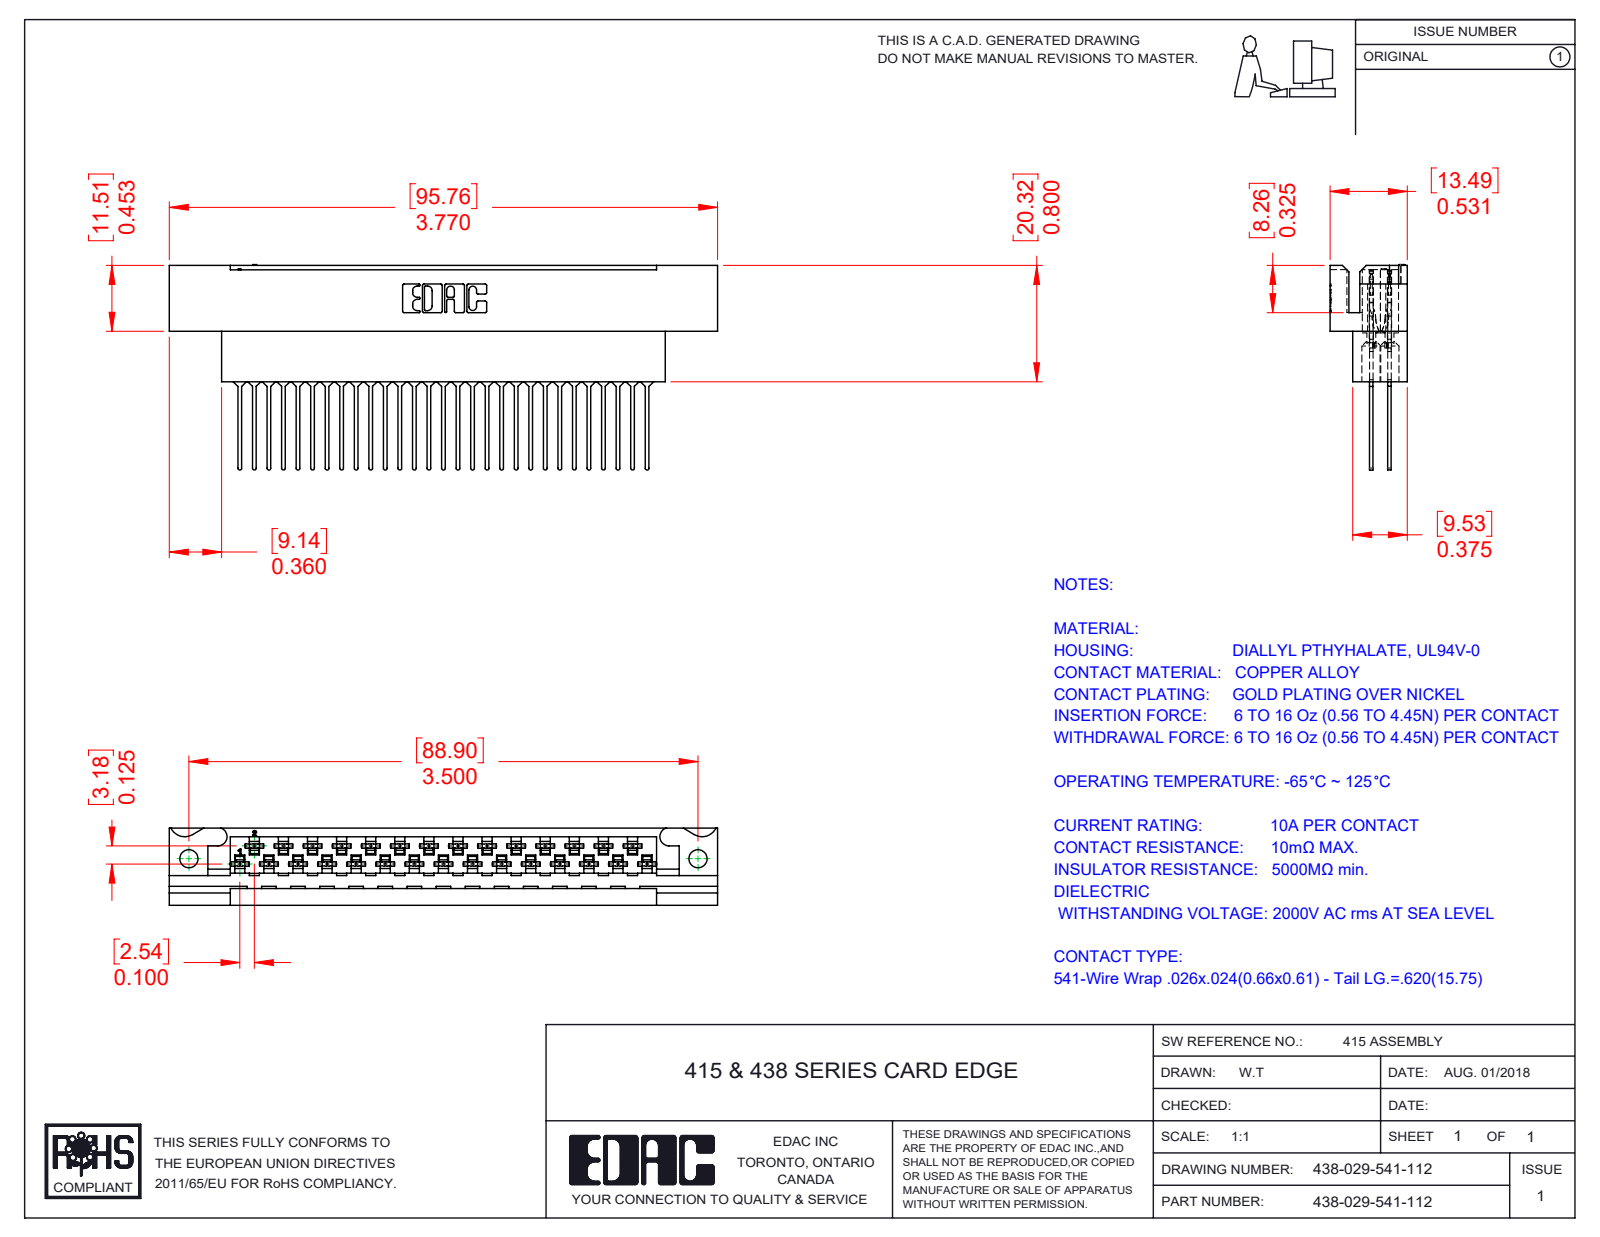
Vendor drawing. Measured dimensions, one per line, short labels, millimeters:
name: 438-210-001_438-210-029-112; 438-029-541-112; 516-290-001_541
written by: SolidWorks 2016 (CONFIG_CONTROL_DESIGN)
unit: mm
bodies: 30 solids, 2998 faces (1911 planar, 804 cylindrical, 283 other)
size: 95.76 × 35.85 × 13.49
volume: 15 636 mm³; area: 19 762 mm²
holes: 29× ⌀1.27, 29× ⌀3.3, 1× ⌀3.17, 1× ⌀3.18
rounds: 116× R0.3, 116× R0.56, 58× R0.18, 58× R0.2, 58× R0.41, 58× R2.03, 29× R0.33, 22× R0.25
face distances: 3.18, 0.61, 1.88, 1.27, 7.49, 13.49, 2.92, 3.96, 6.61, 6.88
hole spacings: 5.08, 10.16, 15.24, 20.32, 25.4, 30.48, 35.56, 2.54
